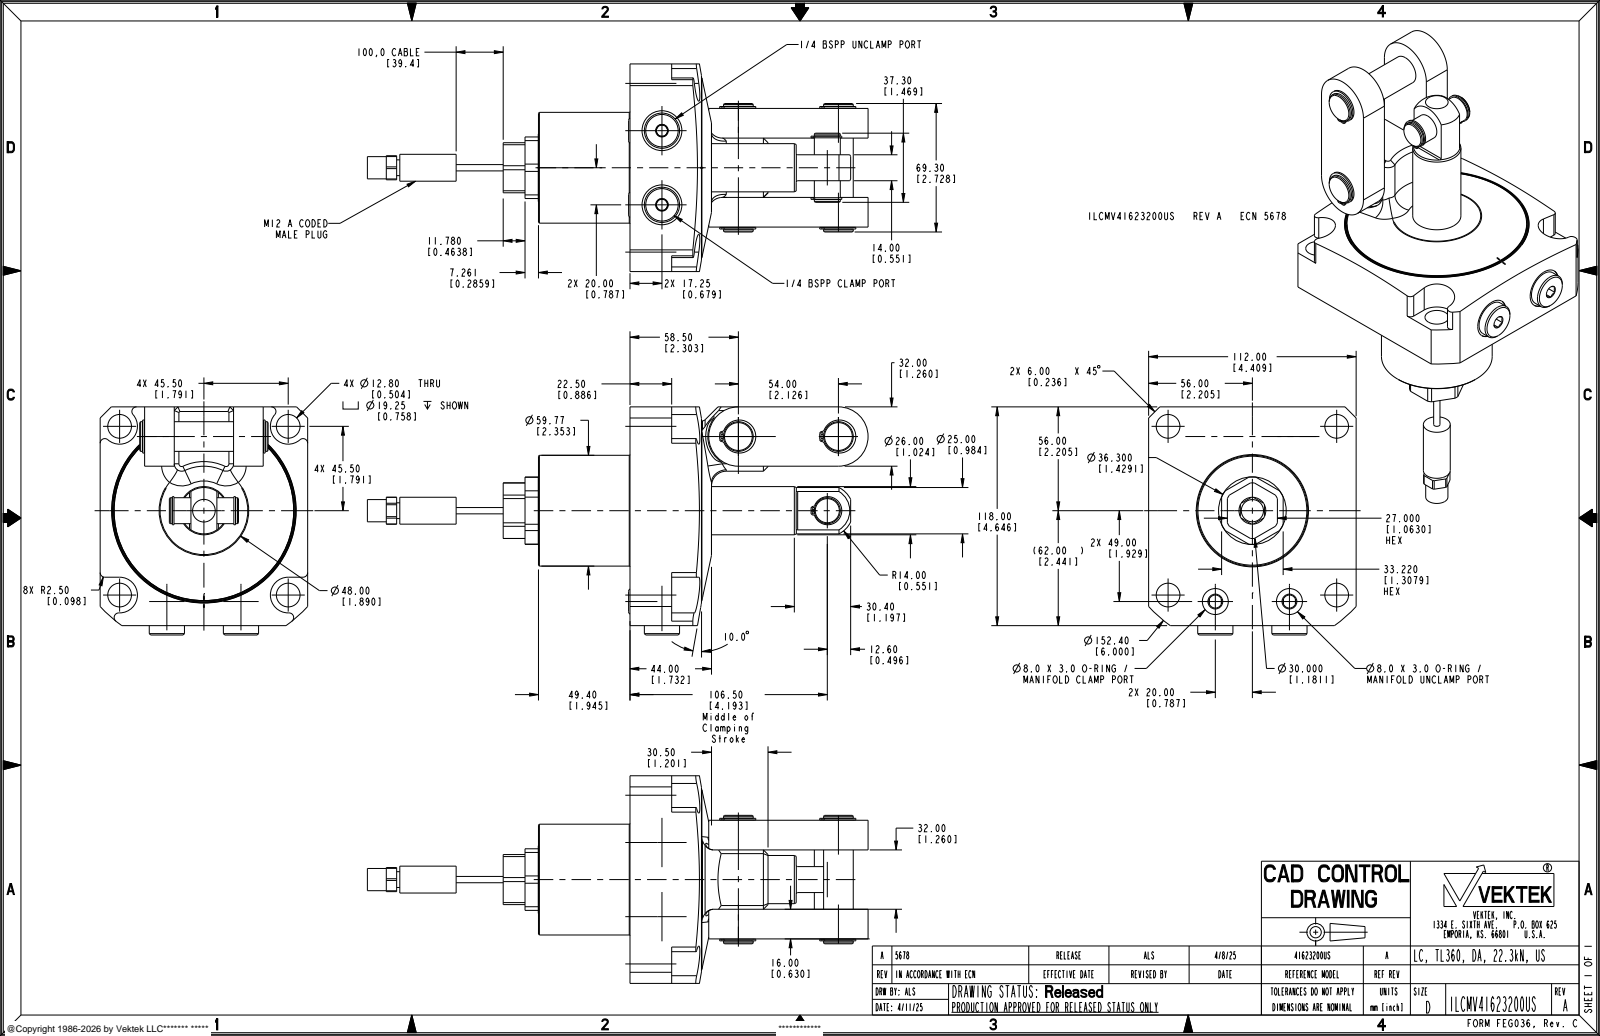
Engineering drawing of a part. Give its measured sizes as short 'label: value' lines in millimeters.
name: ILCMV41623200_BODY_US; ILCMV41623200_LUG_US; ILCMV41623200US
written by: CREO PARAMETRIC BY PTC INC, 2021164 (AUTOMOTIVE_DESIGN)
unit: mm
bodies: 4 solids, 461 faces (168 planar, 201 cylindrical, 92 other)
size: 270.25 × 123.05 × 112
volume: 808 599 mm³; area: 115 472 mm²
holes: 4× ⌀1.19, 4× ⌀12.8, 2× ⌀1.19, 2× ⌀7.04, 2× ⌀11.89, 2× ⌀14, 2× ⌀14.7, 2× ⌀21.5, 1× ⌀97.03
bosses: 2× ⌀19, 2× ⌀17.84, 2× ⌀16, 2× ⌀14.2, 2× ⌀13.16, 2× ⌀11.2, 2× ⌀8, 1× ⌀96.93
rounds: 8× R2.5, 4× R0.8, 4× R1.19, 4× R1.26, 4× R9.62, 2× R0.88, 2× R1.19, 2× R4
face distances: 25.5, 24, 88, 16, 32, 112, 72, 40, 48, 118
hole spacings: 9.03, 64.35, 91, 54, 3.1, 25.74, 40, 45.13
